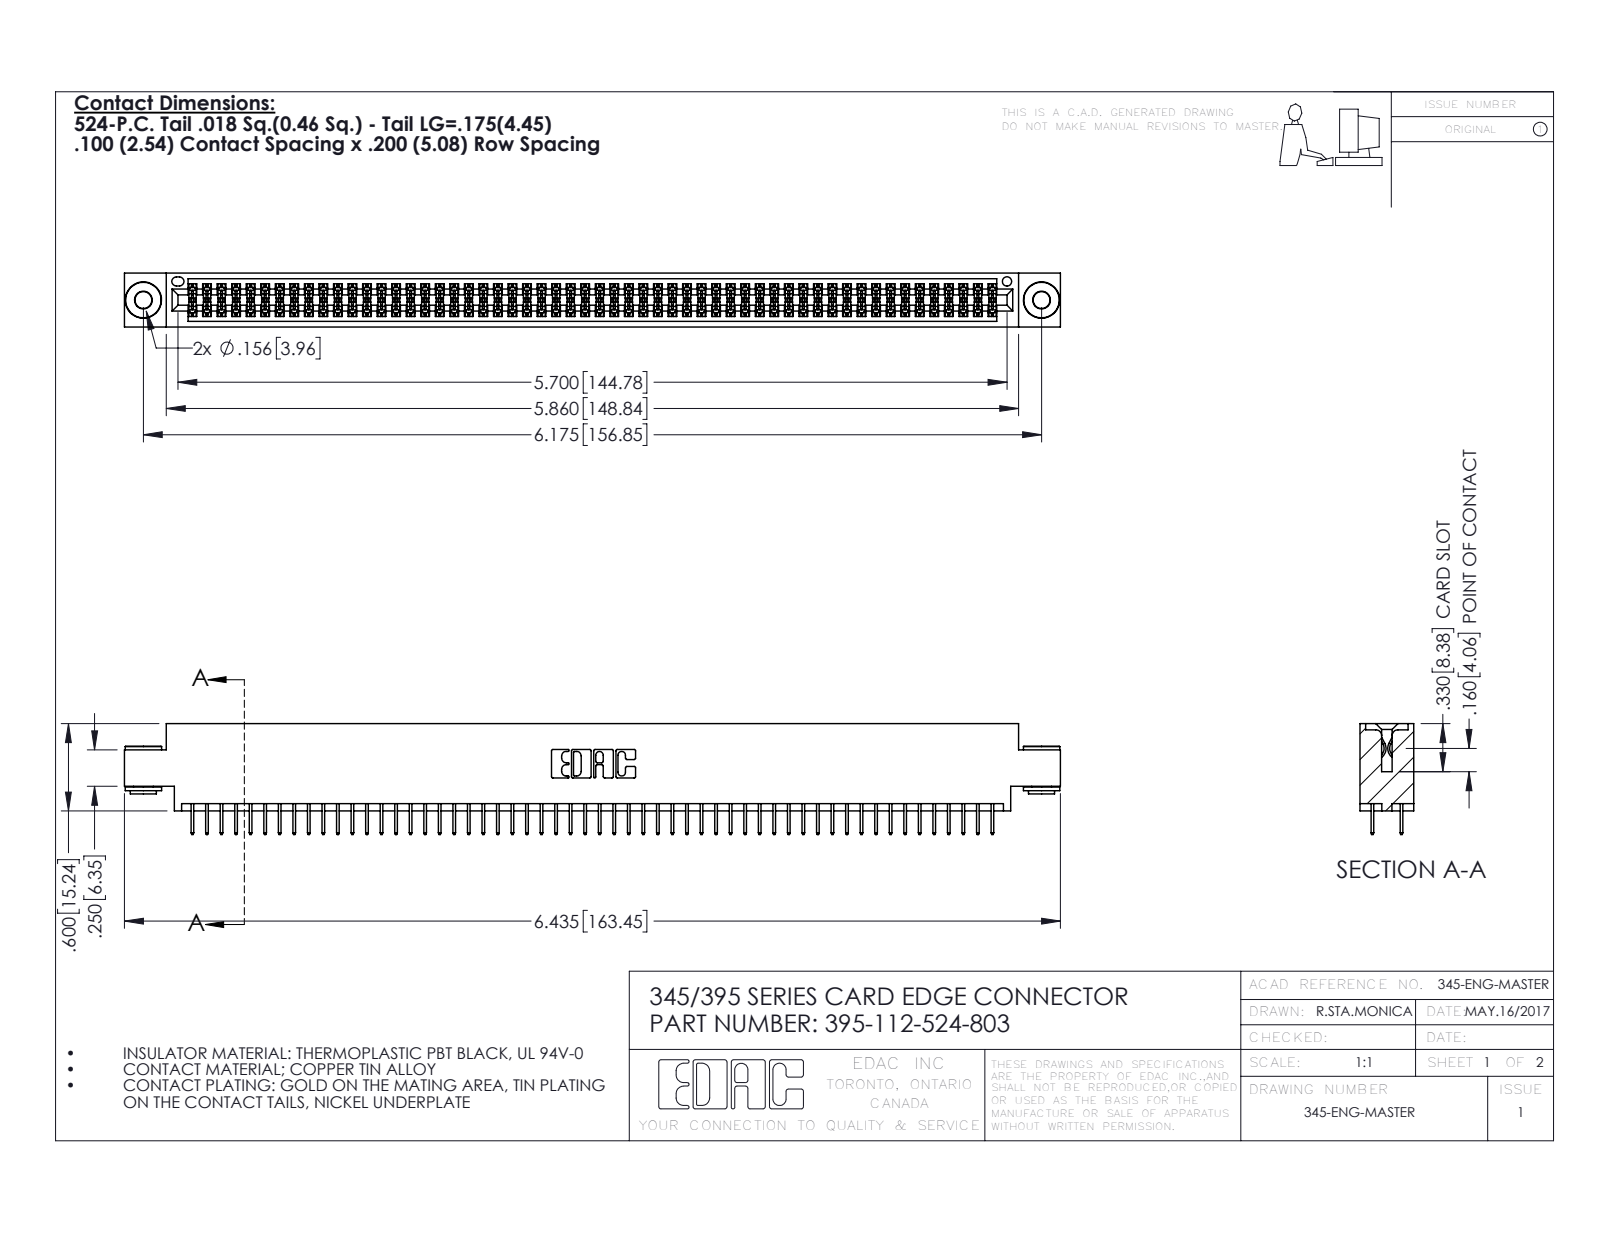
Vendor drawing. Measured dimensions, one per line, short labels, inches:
name: 345-292-001_345-293-124; 345-250-002_345-250-002-102; 345 Part_0.170 Offset - 0.156 Dia-TH; 395-112-524-803
written by: SolidWorks 2016 (CONFIG_CONTROL_DESIGN)
unit: in
bodies: 115 solids, 6216 faces (4462 planar, 1746 cylindrical, 8 other)
size: 6.435 × 0.762 × 0.37
volume: 0.961 in³; area: 36.34 in²
holes: 2× ⌀0.116, 2× ⌀0.156, 1× ⌀0.064
bosses: 2× ⌀0.25, 2× ⌀0.18, 2× ⌀0.136
rounds: 168× R0.006, 22× R0.01, 6× R0.007, 6× R0.031, 3× R0.026, 2× R0.014, 2× R0.019, 2× R0.022
face distances: 0.072, 0.298, 0.37, 0.2, 0.098, 0.272, 0.025, 0.225, 0.175, 0.072
hole spacings: 0.27, 5.939, 6.175
